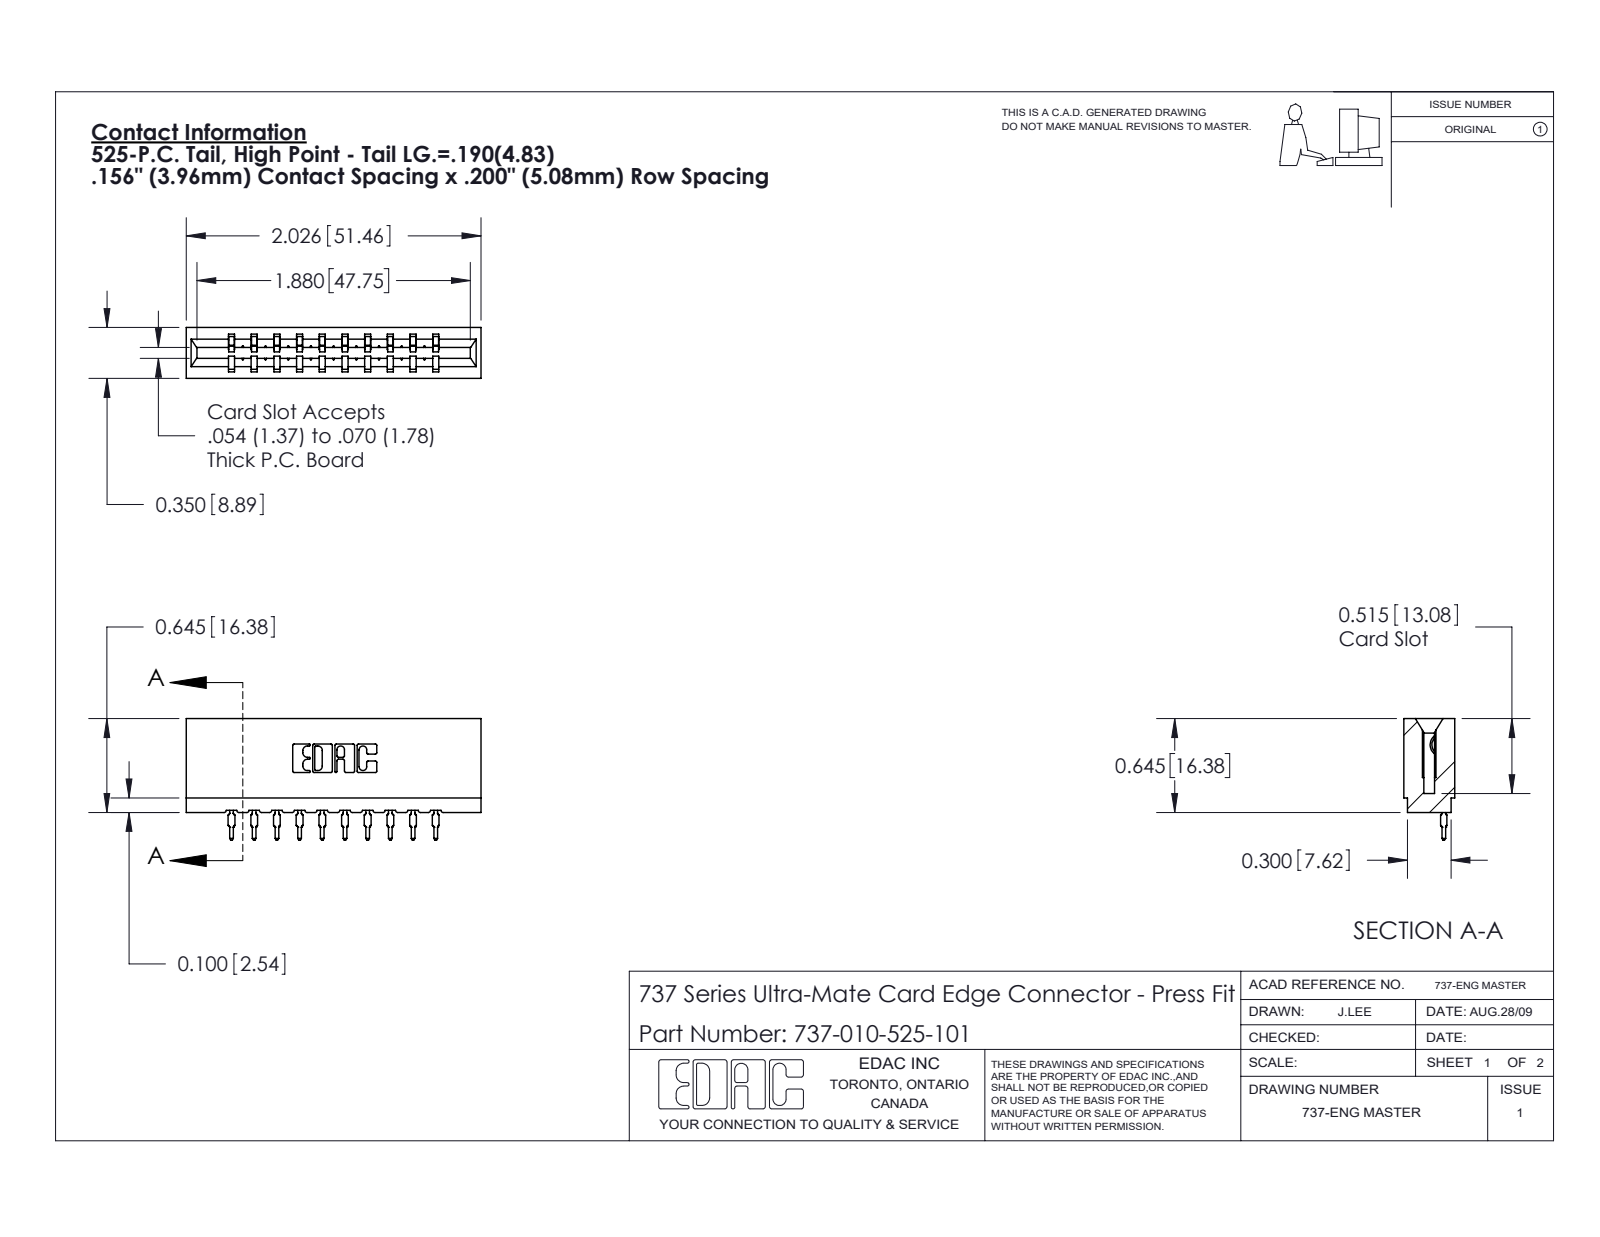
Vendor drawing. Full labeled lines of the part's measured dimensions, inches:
Part name (STEP PRODUCT): 745-292-001_525; 737-010-525-101; 737 Part_Insulator Option - 01
STEP written by: SolidWorks 2020 (CONFIG_CONTROL_DESIGN)
Units: inches
Bodies: 11 solids, 1224 faces (734 planar, 230 cylindrical, 260 other)
Overall size (bounding box): 2.026 × 0.836 × 0.35
Volume: 0.317 in³ · Surface area: 9.845 in²
Partial cylindrical surfaces — rounded edges, fillets, slot ends (radius × count): R0.01 ×22, R0.015 ×20, R0.021 ×20, R0.007 ×6, R0.031 ×6, R0.005 ×4, R0.011 ×4, R0.026 ×3
Main face-to-face distances: 0.156, 0.138, 0.212, 0.35, 0.624, 0.312, 0.354, 0.78, 0.468, 0.198
